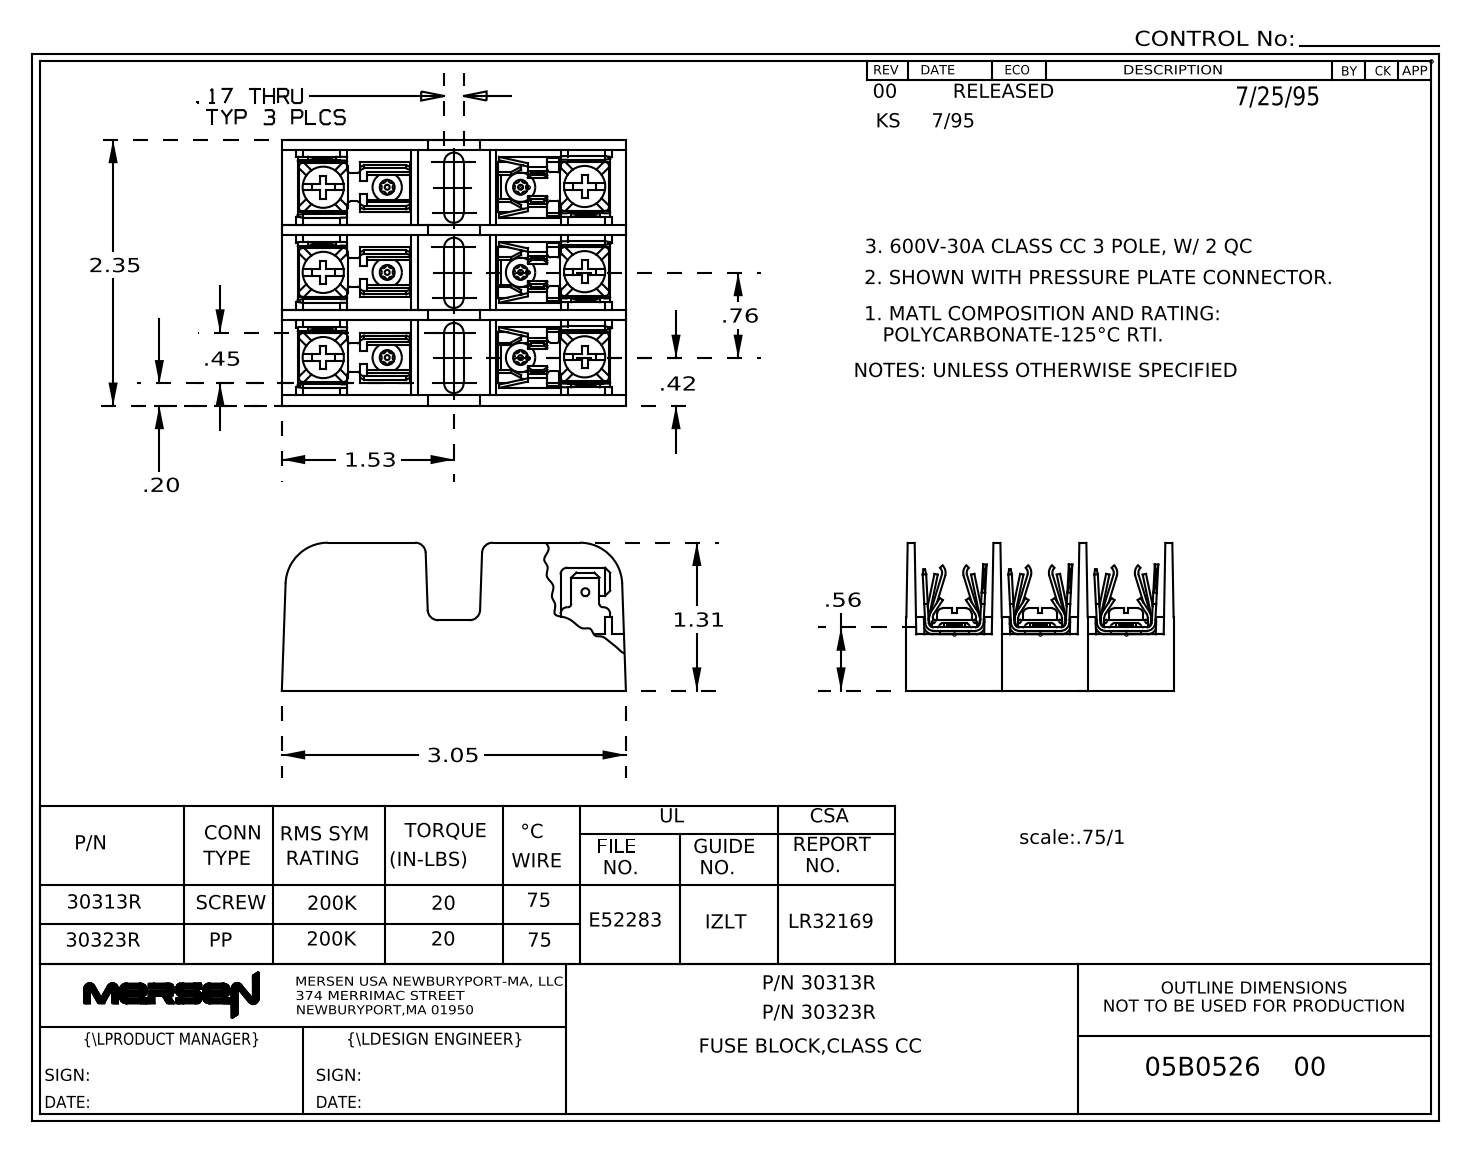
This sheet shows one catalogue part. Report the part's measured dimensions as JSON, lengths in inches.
{"part_name": "05B0526r00", "step_written_by": "SolidWorks 2013 (AUTOMOTIVE_DESIGN)", "units": "inches", "bodies": {"solids": 27, "faces": 2816, "planar": 1374, "cylindrical": 928, "other": 514}, "overall_size": [3.05, 2.36, 1.31], "volume_in3": 3.273, "surface_area_in2": 91.48, "round_holes": [[0.07, 6], [0.101, 6], [0.14, 6], [0.2, 6], [0.15, 3], [0.156, 3], [0.19, 3], [0.24, 2]], "round_bosses_or_shafts": [[0.365, 6], [0.27, 6], [0.138, 6], [0.099, 6], [0.047, 6], [0.19, 3], [0.225, 2], [0.225, 2]], "partial_cylinders_radius": [[0.02, 42], [0.07, 42], [0.012, 36], [0.02, 36], [0.03, 34], [0.093, 27], [0.06, 21], [0.019, 19]], "face_to_face_distances": [0.755, 0.062, 0.5, 0.062, 1.51, 0.76, 0.693, 0.04, 1.823, 0.755], "hole_center_spacings": [0.944, 0.567, 1.757, 0.755, 1.409, 1.912, 0.755, 1.19]}
